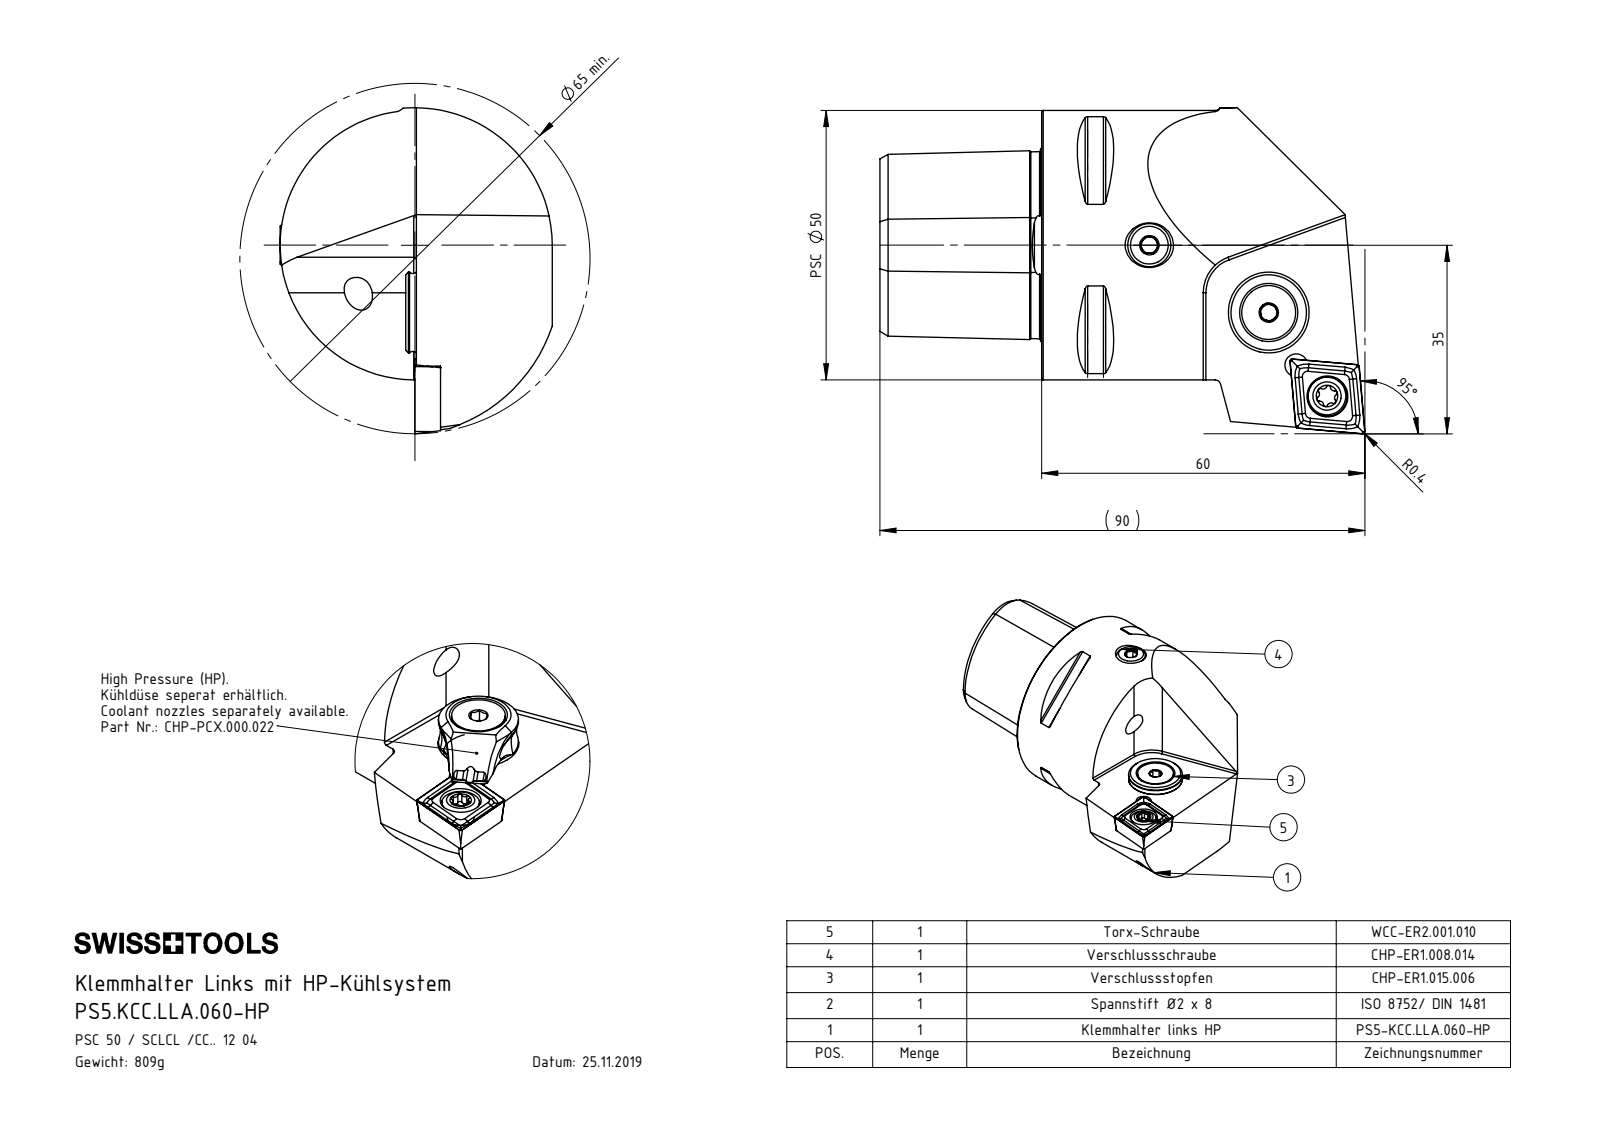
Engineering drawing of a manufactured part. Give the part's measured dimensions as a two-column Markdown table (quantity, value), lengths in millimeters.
| quantity | value |
| --- | --- |
| part name | ISO 8752 2x8; PS5.KCC.LLA.060-HP; CHP-ER1.008.014_A; WCC-ER2.001.010_A (+6 more) |
| STEP written by | SolidWorks 2017 (AUTOMOTIVE_DESIGN) |
| units | millimeters |
| bodies | 8 solids, 376 faces (88 planar, 102 cylindrical, 186 other) |
| overall size | 90 × 60.5 × 50.5 |
| volume | 103 358 mm³ |
| surface area | 22 748 mm² |
| round holes (diameter × count) | 4.2 × 4, 5 × 2, 1.2 × 1, 2 × 1, 2.5 × 1, 3 × 1, 4 × 1, 5.2 × 1, 5.5 × 1, 6.1 × 1, 7 × 1, 7.6 × 1 |
| round bosses / shafts (diameter × count) | 5 × 2, 50 × 1, 15 × 1, 13.4 × 1, 10 × 1, 8 × 1, 7 × 1, 5.5 × 1 |
| partial cylindrical surfaces (radius × count) | 0.5 × 10, 0.39 × 6, 0.69 × 3, 0.69 × 3, 4 × 1, 7 × 1, 25.5 × 1, 30 × 1 |
| main face-to-face distances | 30, 25.2, 60, 20.7, 4.5, 20.74, 4.46, 19.18, 44.4, 20 |
| hole center spacings | 4.49, 8, 8.09, 8.2, 8.78, 11.01, 15.83, 15.94 |
